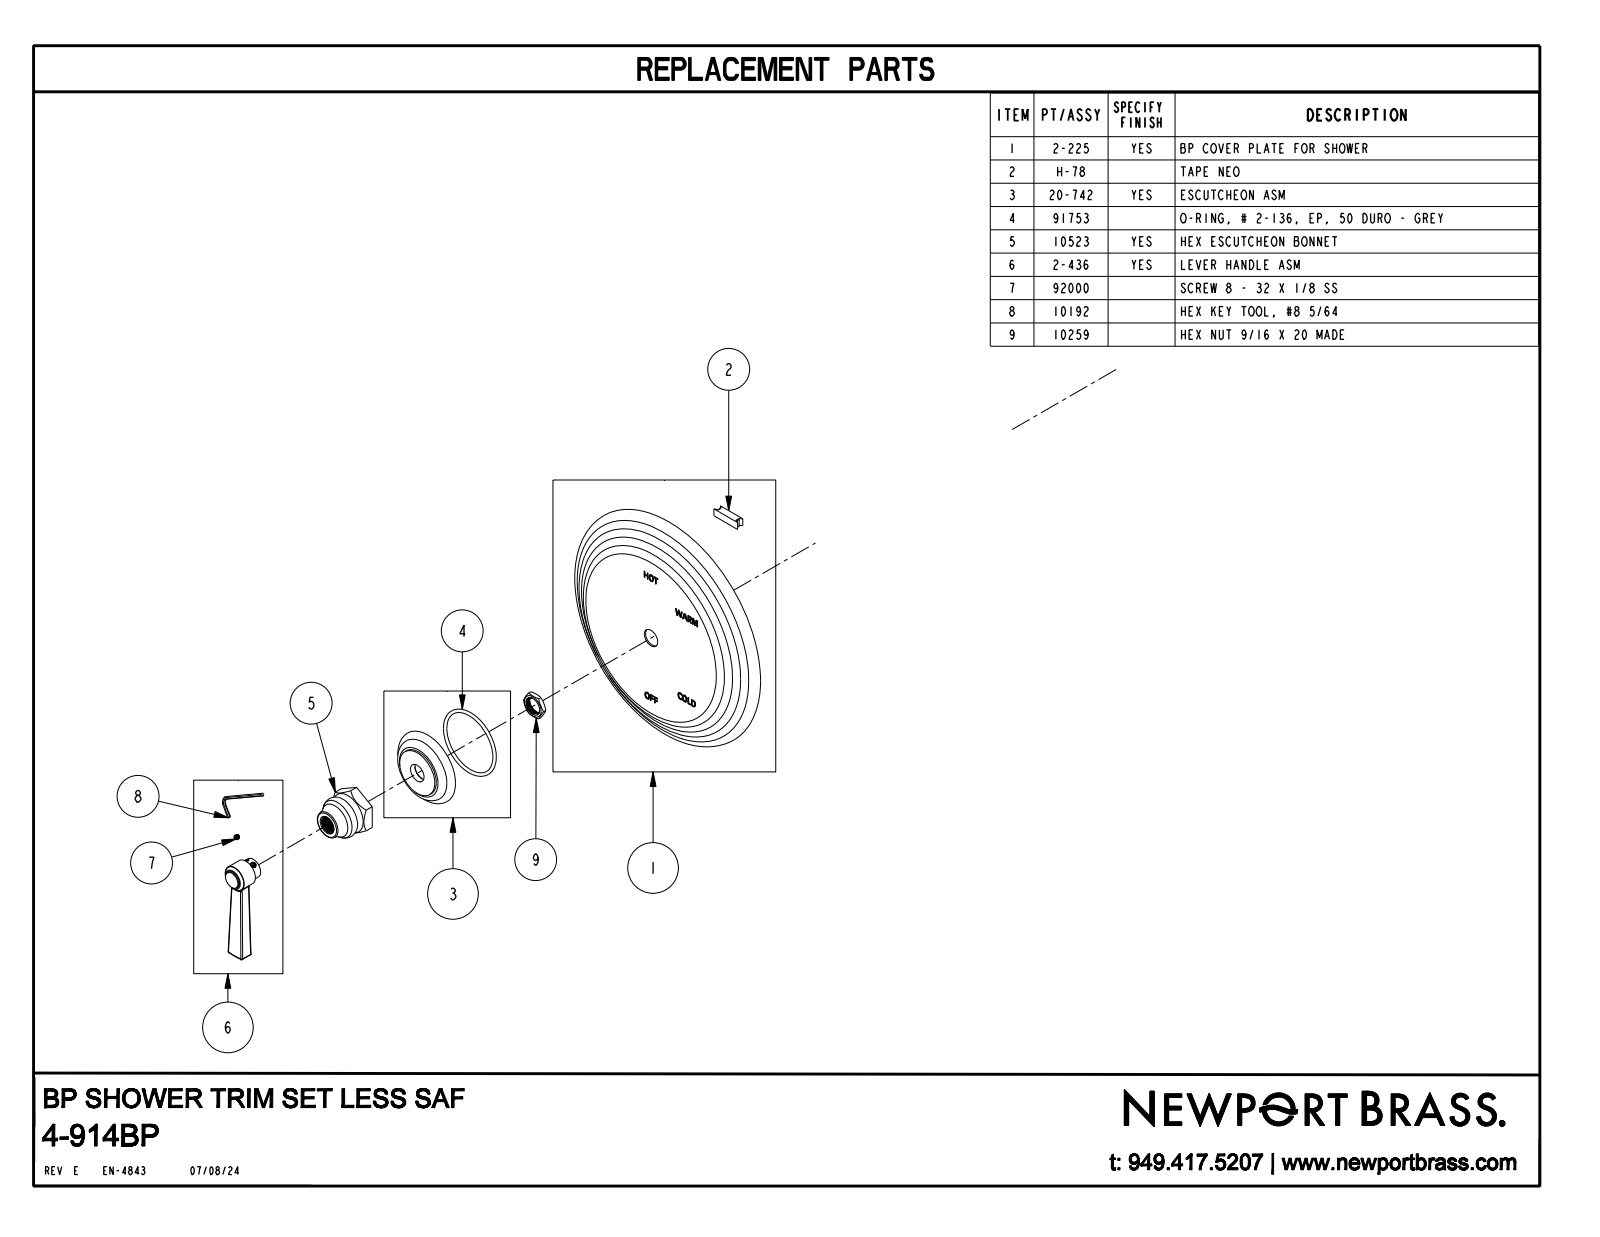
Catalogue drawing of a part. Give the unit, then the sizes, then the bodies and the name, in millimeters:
Units: millimetres
Overall size (bounding box): 196.9 × 196.9 × 85.3
Round bosses / shafts (diameter × count): ⌀37.6 ×1, ⌀20.3 ×1, ⌀15.9 ×1, ⌀13.3 ×1, ⌀10.2 ×1
Partial cylindrical surfaces — rounded edges, fillets, slot ends (radius × count): R1 ×2, R1.4 ×2
Main face-to-face distances: 19.2, 33.4, 62, 42.8, 28.7, 9.5, 33.3, 19.1, 9.6, 43
Volume: 514 400 mm³ · Surface area: 73 870 mm²
Bodies: 1 solid, 303 faces (151 planar, 14 cylindrical, 138 other)
Part name (STEP PRODUCT): 4-914BP
STEP written by: CREO PARAMETRIC BY PTC INC, 2018400 (CONFIG_CONTROL_DESIGN)
